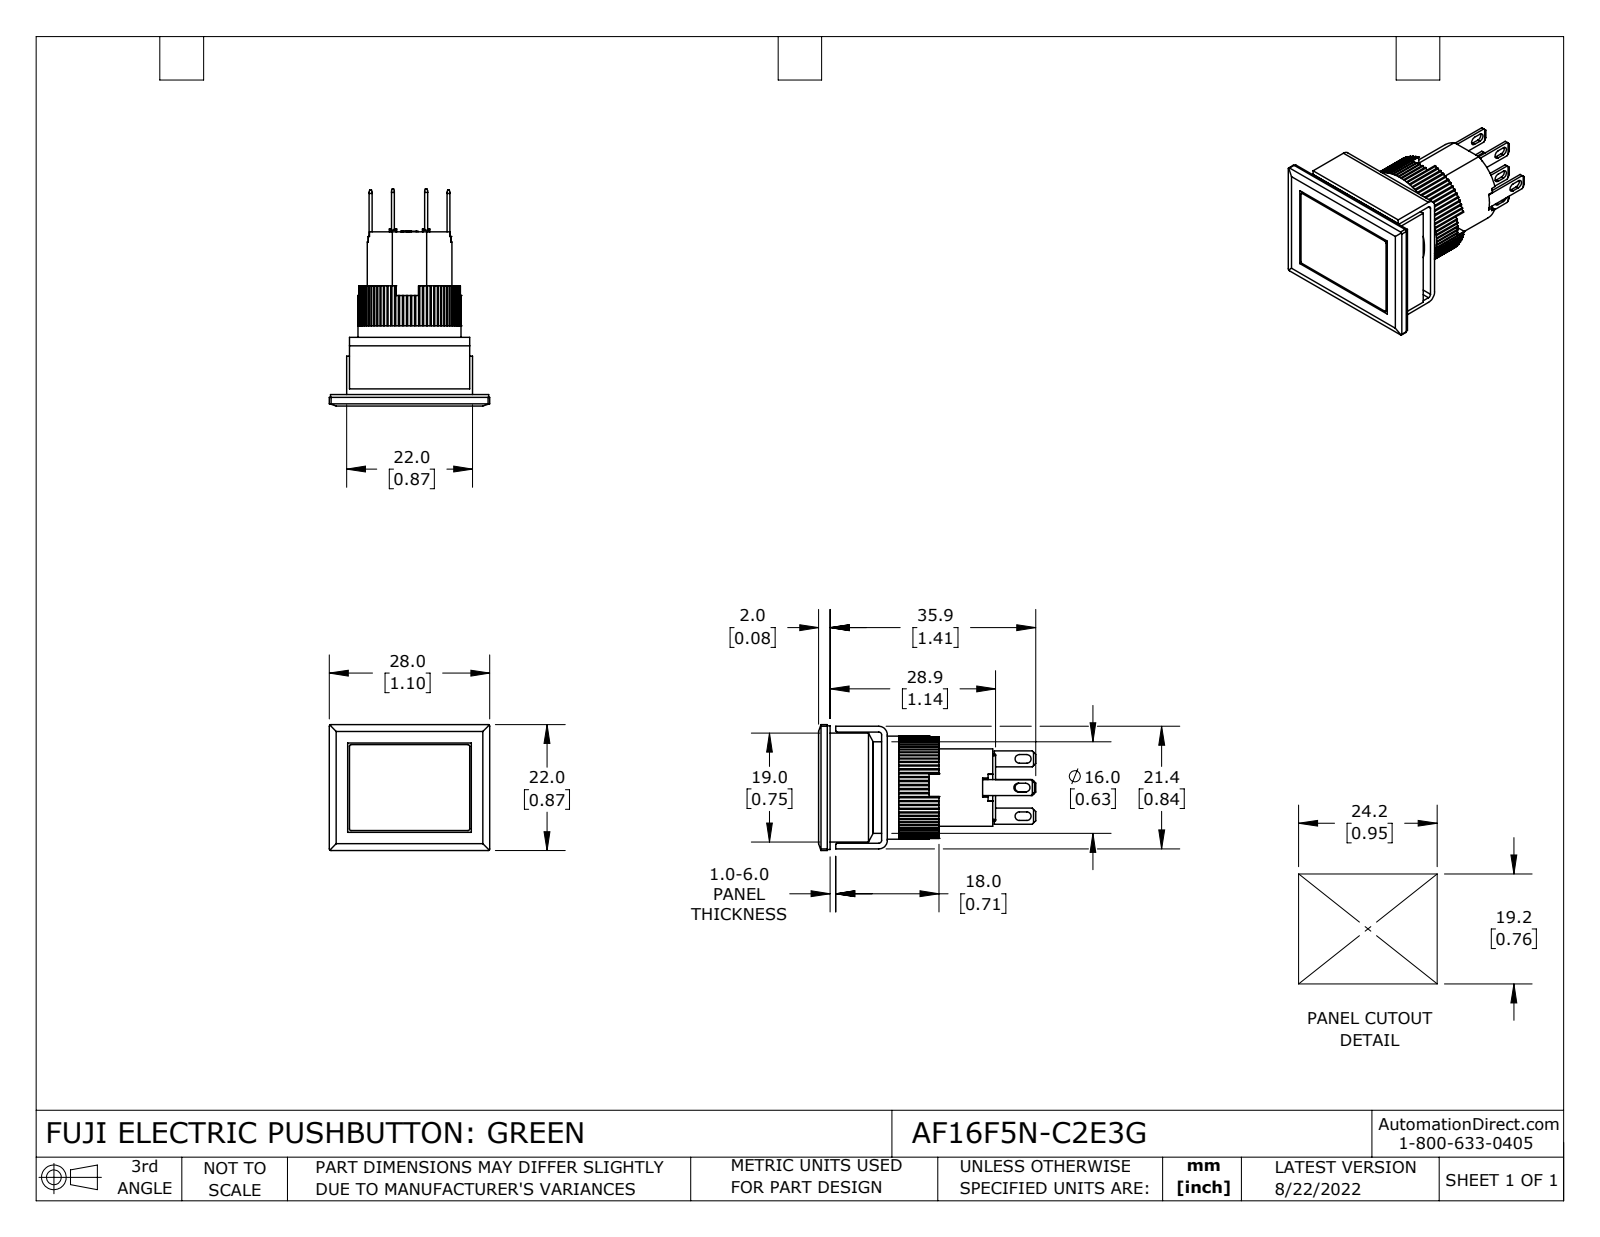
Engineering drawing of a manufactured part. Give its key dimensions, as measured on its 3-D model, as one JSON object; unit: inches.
{"part_name": "AF16F5N-C2E3G", "step_written_by": "SolidWorks 2021 (CONFIG_CONTROL_DESIGN)", "units": "inches", "bodies": {"solids": 14, "faces": 828, "planar": 644, "cylindrical": 182, "other": 2}, "overall_size": [1.492, 1.102, 0.866], "volume_in3": 0.543, "surface_area_in2": 12.03, "round_holes": [[0.039, 1], [0.709, 1]], "round_bosses_or_shafts": [[0.63, 1], [0.583, 1]], "partial_cylinders_radius": [[0.01, 80], [0.008, 12], [0.012, 8], [0.03, 8], [0.02, 2], [0.059, 2]], "face_to_face_distances": [0.374, 0.059, 0.02, 0.142, 0.039, 0.315, 0.232, 0.083, 0.079, 0.756]}
